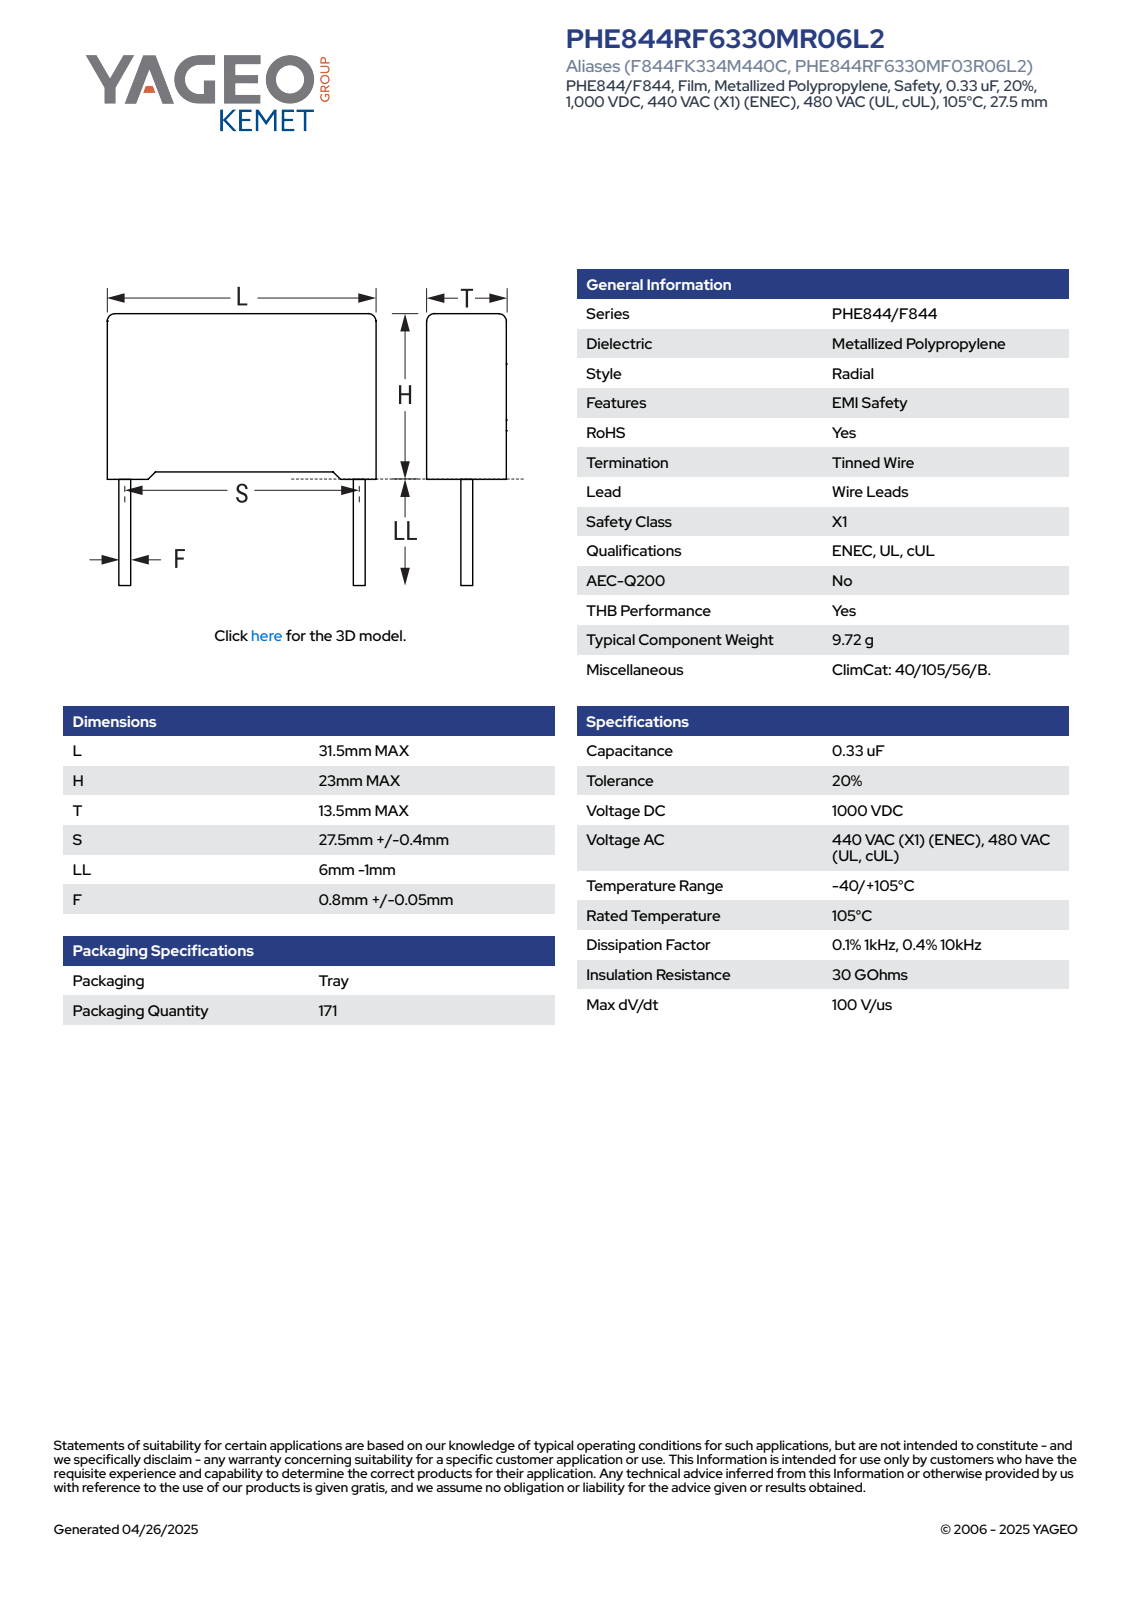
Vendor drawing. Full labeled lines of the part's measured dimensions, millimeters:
Part name (STEP PRODUCT): CFR_RB2_31.5X23X13.5_L31.5H23T13.5S27.5LL5F0.85
STEP written by: SolidWorks 2021 (AUTOMOTIVE_DESIGN)
Units: millimetres
Bodies: 4 solids, 85 faces (77 planar, 8 cylindrical, 0 other)
Overall size (bounding box): 31.5 × 28 × 13.51
Volume: 9 481 mm³ · Surface area: 2 996 mm²
Round bosses / shafts (diameter × count): ⌀0.85 ×2
Partial cylindrical surfaces — rounded edges, fillets, slot ends (radius × count): R0.5 ×4
Main face-to-face distances: 13.5, 22.21, 31.5, 22.25, 0.75, 0.79, 23, 1.05, 30.45, 12.45
